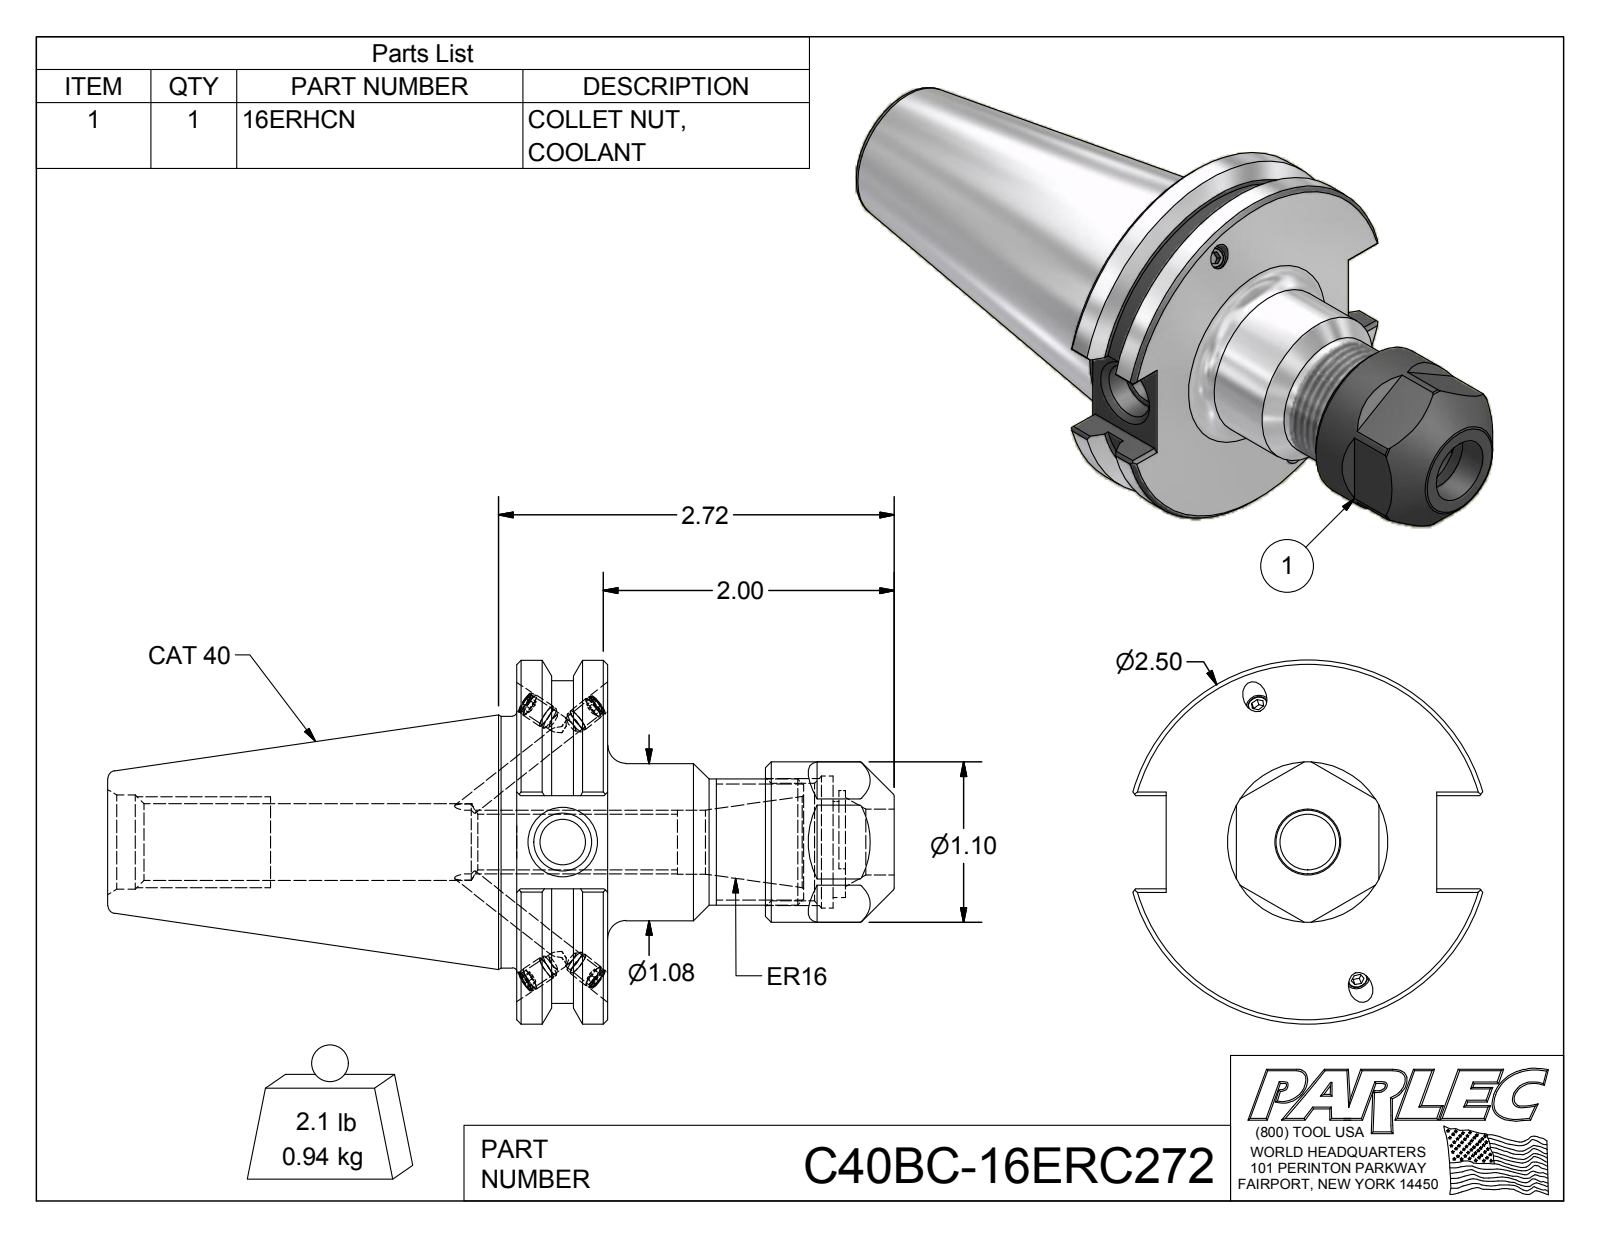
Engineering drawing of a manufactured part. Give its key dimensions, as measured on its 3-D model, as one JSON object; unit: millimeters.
{"part_name": "C40BC-16ERC272; C40BCB-16ER2-1; 029-965; 16ERHCN", "step_written_by": "Autodesk Inventor 2012 (AUTOMOTIVE_DESIGN)", "units": "millimeters", "bodies": {"solids": 6, "faces": 184, "planar": 93, "cylindrical": 41, "other": 50}, "overall_size": [137.4, 63.5, 61], "volume_mm3": 120200, "surface_area_mm2": 28720, "round_holes": [[3.3, 4], [4.1, 4], [8, 1], [9.7, 1], [10.1, 1], [11.2, 1], [11.5, 1], [13.4, 1], [16.5, 1], [16.8, 1], [20.5, 1], [23, 1]], "round_bosses_or_shafts": [[4.2, 4], [4, 4], [63.5, 1], [56.4, 1], [43.9, 1], [28, 1], [27.4, 1], [22, 1]], "partial_cylinders_radius": [[9, 1]], "face_to_face_distances": [15.9, 24.9, 55.2, 39.3, 16.3, 47.2, 43.4, 27.5, 11.8, 71.5], "hole_center_spacings": [1.3]}
